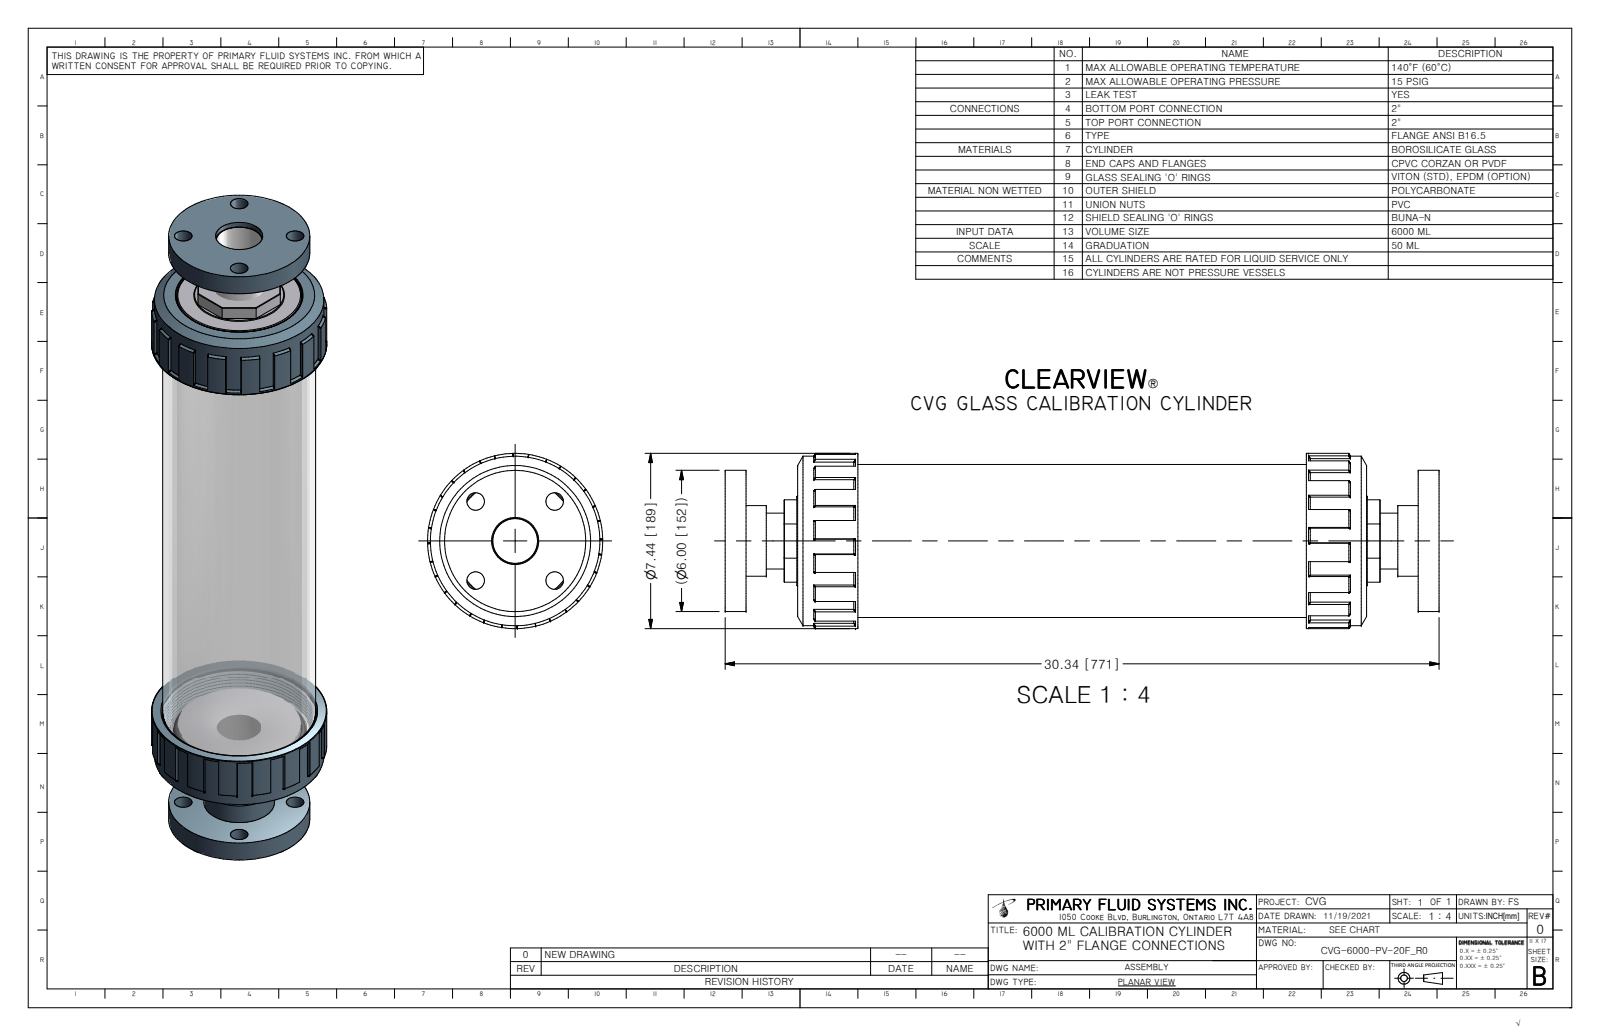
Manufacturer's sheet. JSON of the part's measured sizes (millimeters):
{"step_written_by": "Autodesk Inventor 2009 (AUTOMOTIVE_DESIGN)", "units": "millimeters", "bodies": {"solids": 1, "faces": 379, "planar": 142, "cylindrical": 97, "other": 140}, "overall_size": [770.6, 189.1, 189.1], "volume_mm3": 937000, "surface_area_mm2": 1612000, "round_holes": [[18.9, 4], [48.3, 1], [49.3, 1], [50.8, 1], [56.4, 1], [135, 1], [136.8, 1], [145, 1], [146.3, 1], [151.6, 1], [166, 1]], "round_bosses_or_shafts": [[189.1, 1], [182.9, 1], [165.1, 1], [165, 1], [159, 1], [158.8, 1], [152.4, 1], [134.6, 1]], "partial_cylinders_radius": [[8.5, 2], [85.9, 2]], "face_to_face_distances": [22.5, 748.1, 78.2, 692.4, 55.8, 669.9, 770.6, 725.7, 614.1, 143.2], "hole_center_spacings": [60.3, 85.3, 120.7]}
